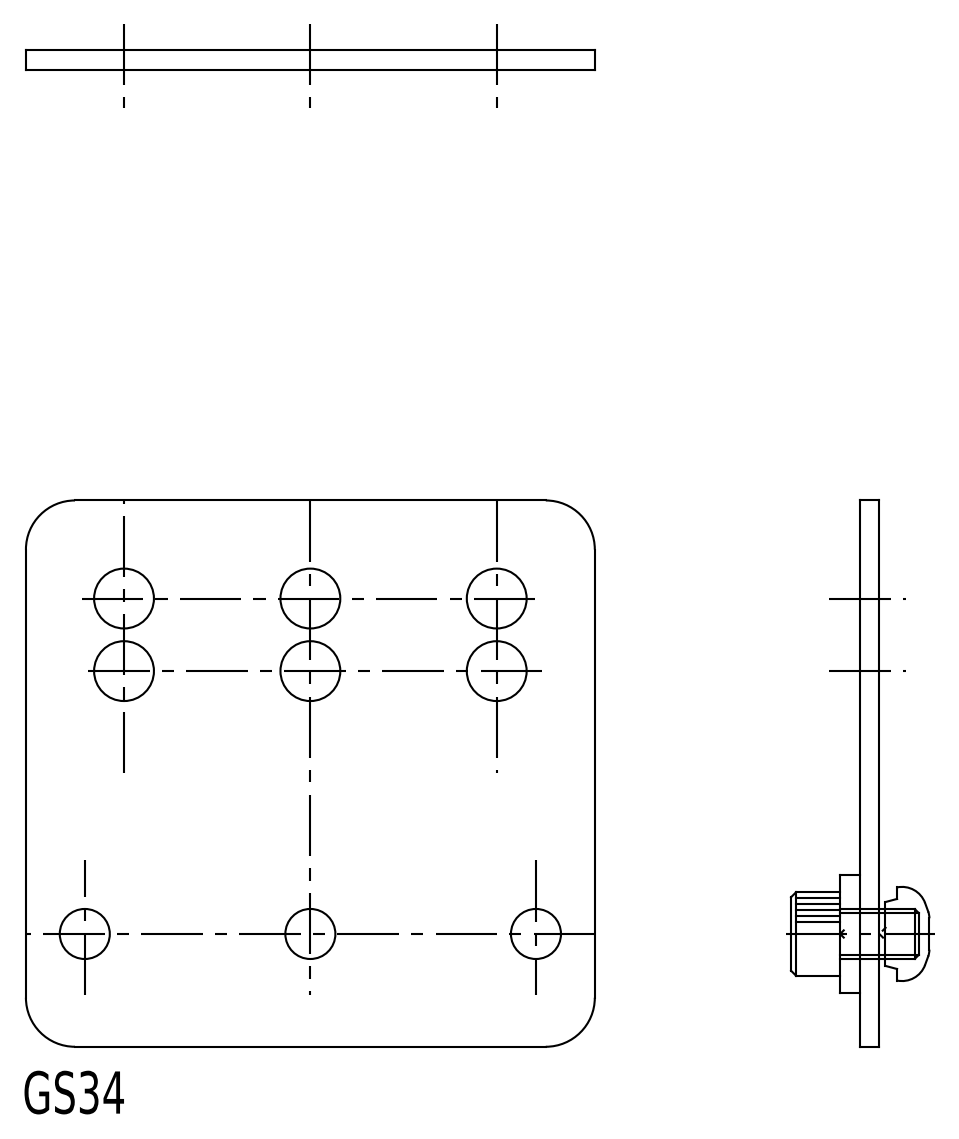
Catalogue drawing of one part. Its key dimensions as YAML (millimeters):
part_name: "GS34"
step_written_by: "Spatial InterOp 3D (automotive_design)"
units: millimeters
bodies: {solids: 1, faces: 19, planar: 6, cylindrical: 13, other: 0}
overall_size: [58, 55.7, 2]
volume: 5945
surface_area: 6709
round_holes:
  - {diameter: 6.1, count: 6}
  - {diameter: 5.1, count: 3}
partial_cylinders:
  - {radius: 5, count: 4}
face_to_face_distances: [2, 55.7, 58]
hole_center_spacings: [19, 20.39, 7.4, 23, 27.1, 32.85, 34.43, 35.32]
